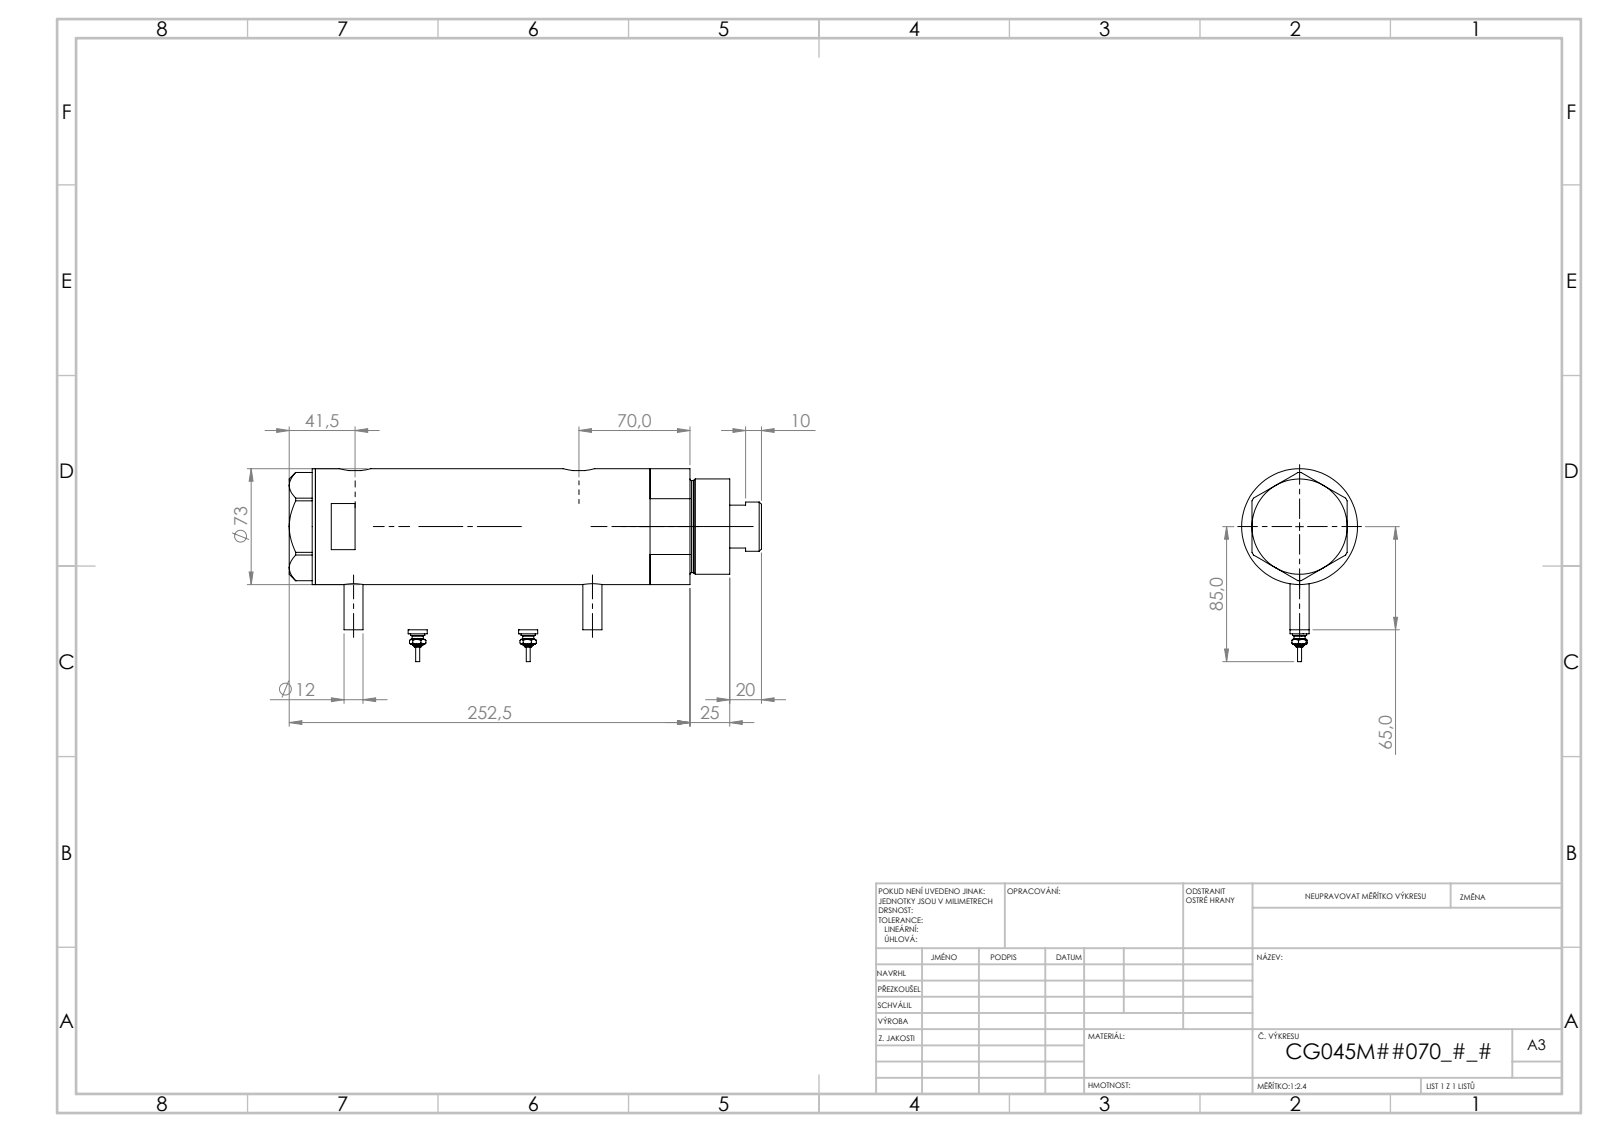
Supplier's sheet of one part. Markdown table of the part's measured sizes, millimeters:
| quantity | value |
| --- | --- |
| part name | V270CG_FRONT; V270CG_MIDDLE; V270CG_BACK; V270CG_SWITCH (+1 more) |
| STEP written by | SolidWorks 2019 (CONFIG_CONTROL_DESIGN) |
| units | millimeters |
| bodies | 6 solids, 231 faces (78 planar, 79 cylindrical, 74 other) |
| overall size | 261.52 × 105.3 × 73 |
| volume | 907 556 mm³ |
| surface area | 154 874 mm² |
| round holes (diameter × count) | 5 × 2, 12.5 × 2, 13.16 × 2, 10.5 × 1, 32 × 1, 33.5 × 1, 45 × 1, 48 × 1, 64 × 1 |
| round bosses / shafts (diameter × count) | 12 × 3, 9 × 2, 7 × 2, 4.34 × 2, 2.4 × 2, 73 × 1, 60 × 1, 58 × 1 |
| partial cylindrical surfaces (radius × count) | 10 × 2 |
| main face-to-face distances | 137.15, 42.5, 153.65, 111.15, 16.5, 16.51, 26, 25.99, 137.14, 225.02 |
| hole center spacings | 121.65, 0.99, 1, 8.5, 8.51, 112.15, 113.14, 113.15 |
